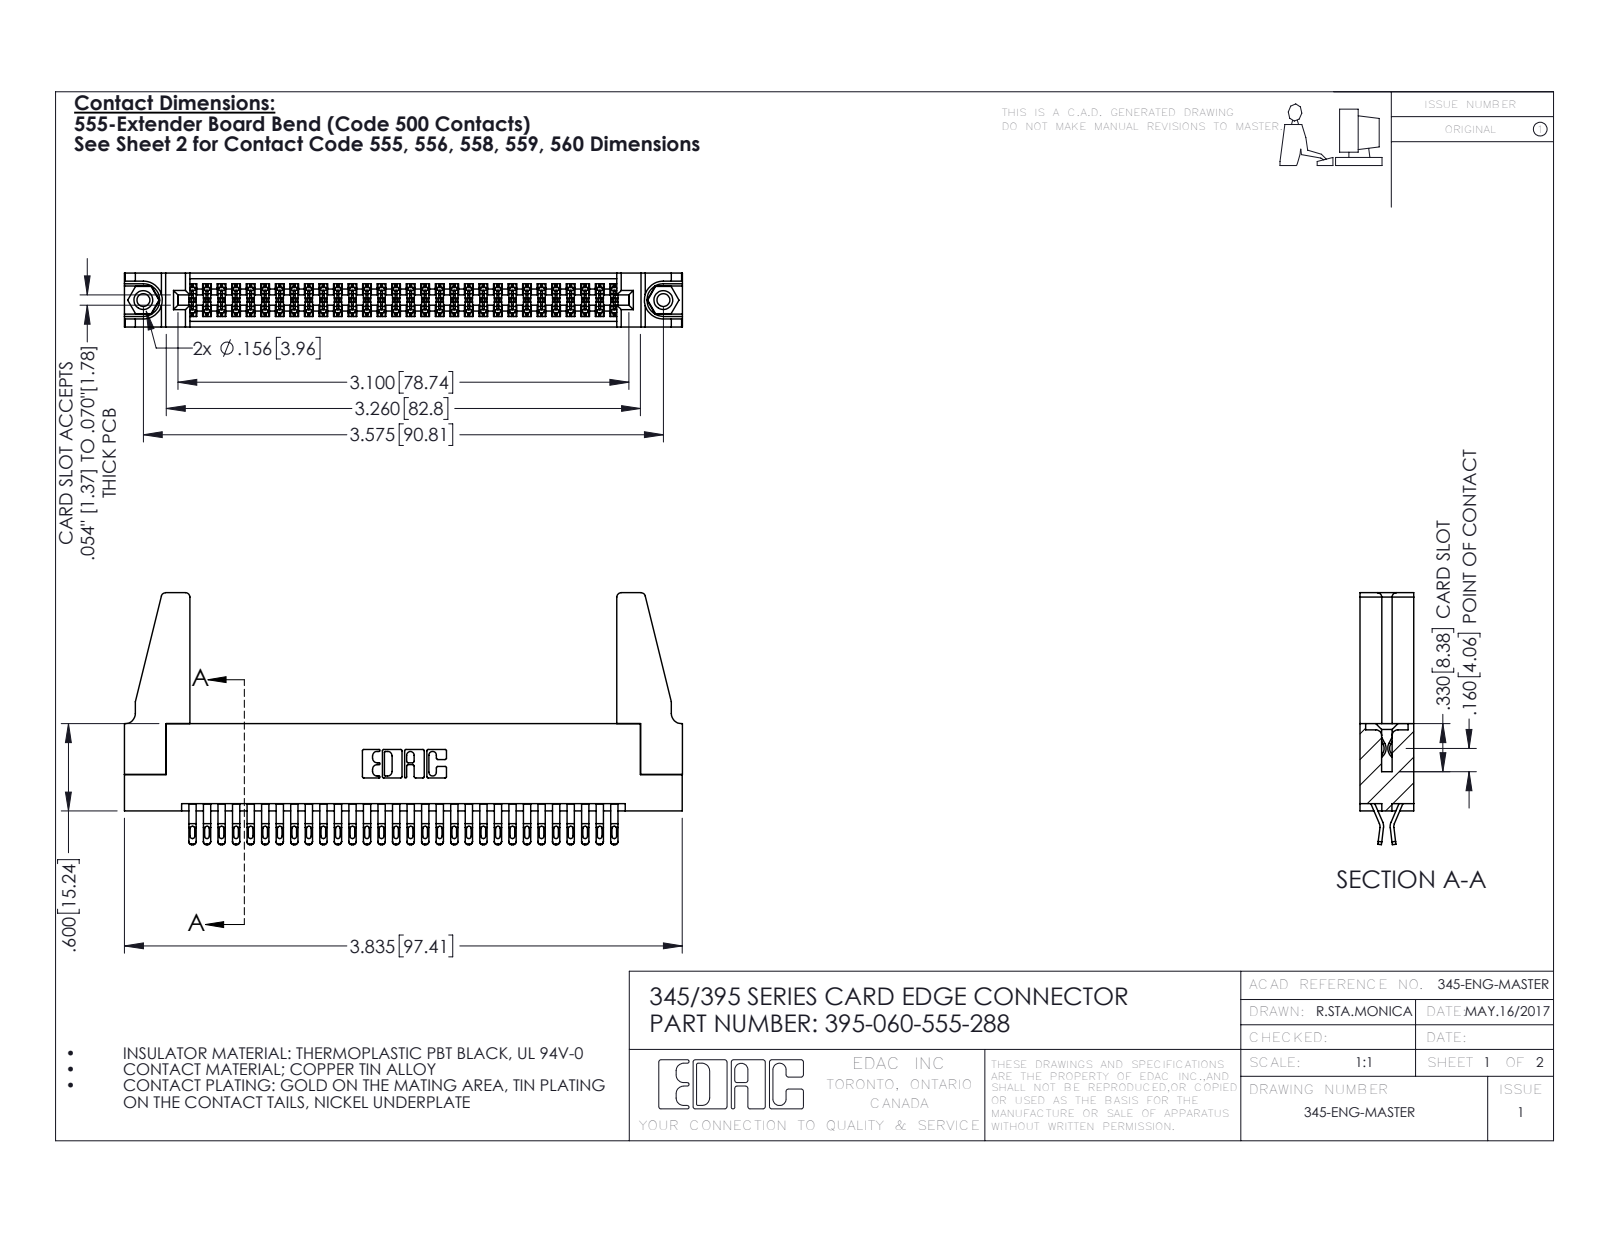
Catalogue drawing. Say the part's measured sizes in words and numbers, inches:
The part is named "395-060-555-288; 345-220-078_345-220-088; 345-250-001_345-250-001-102; 345-292-001_555 Tail (+1 more)". Its 3-D file was written by "SolidWorks 2016 (CONFIG_CONTROL_DESIGN)". It is 65 solids with 3610 faces: 2012 planar, 1582 cylindrical and 16 other. Overall it measures 3.836 by 1.732 by 0.37 inches. Its volume is 0.78 cubic inches and its surface area 27.25 square inches. Round holes: 2 of diameter 0.089, 2 of diameter 0.125, 2 of diameter 0.156, 1 of diameter 0.064. Round bosses or shafts: 2 of diameter 0.155. Partial cylindrical surfaces (rounded edges, fillets, slot ends): 150 of radius 0.016, 120 of radius 0.02, 90 of radius 0.006, 22 of radius 0.01, 8 of radius 0.03, 6 of radius 0.007, 6 of radius 0.031, 3 of radius 0.026. The main face-to-face distances are 0.072, 0.298, 0.37, 0.2, 0.025, 0.098, 0.272, 0.225, 0.175, 0.149. The hole center spacings are 0.27, 3.34, 3.575.
